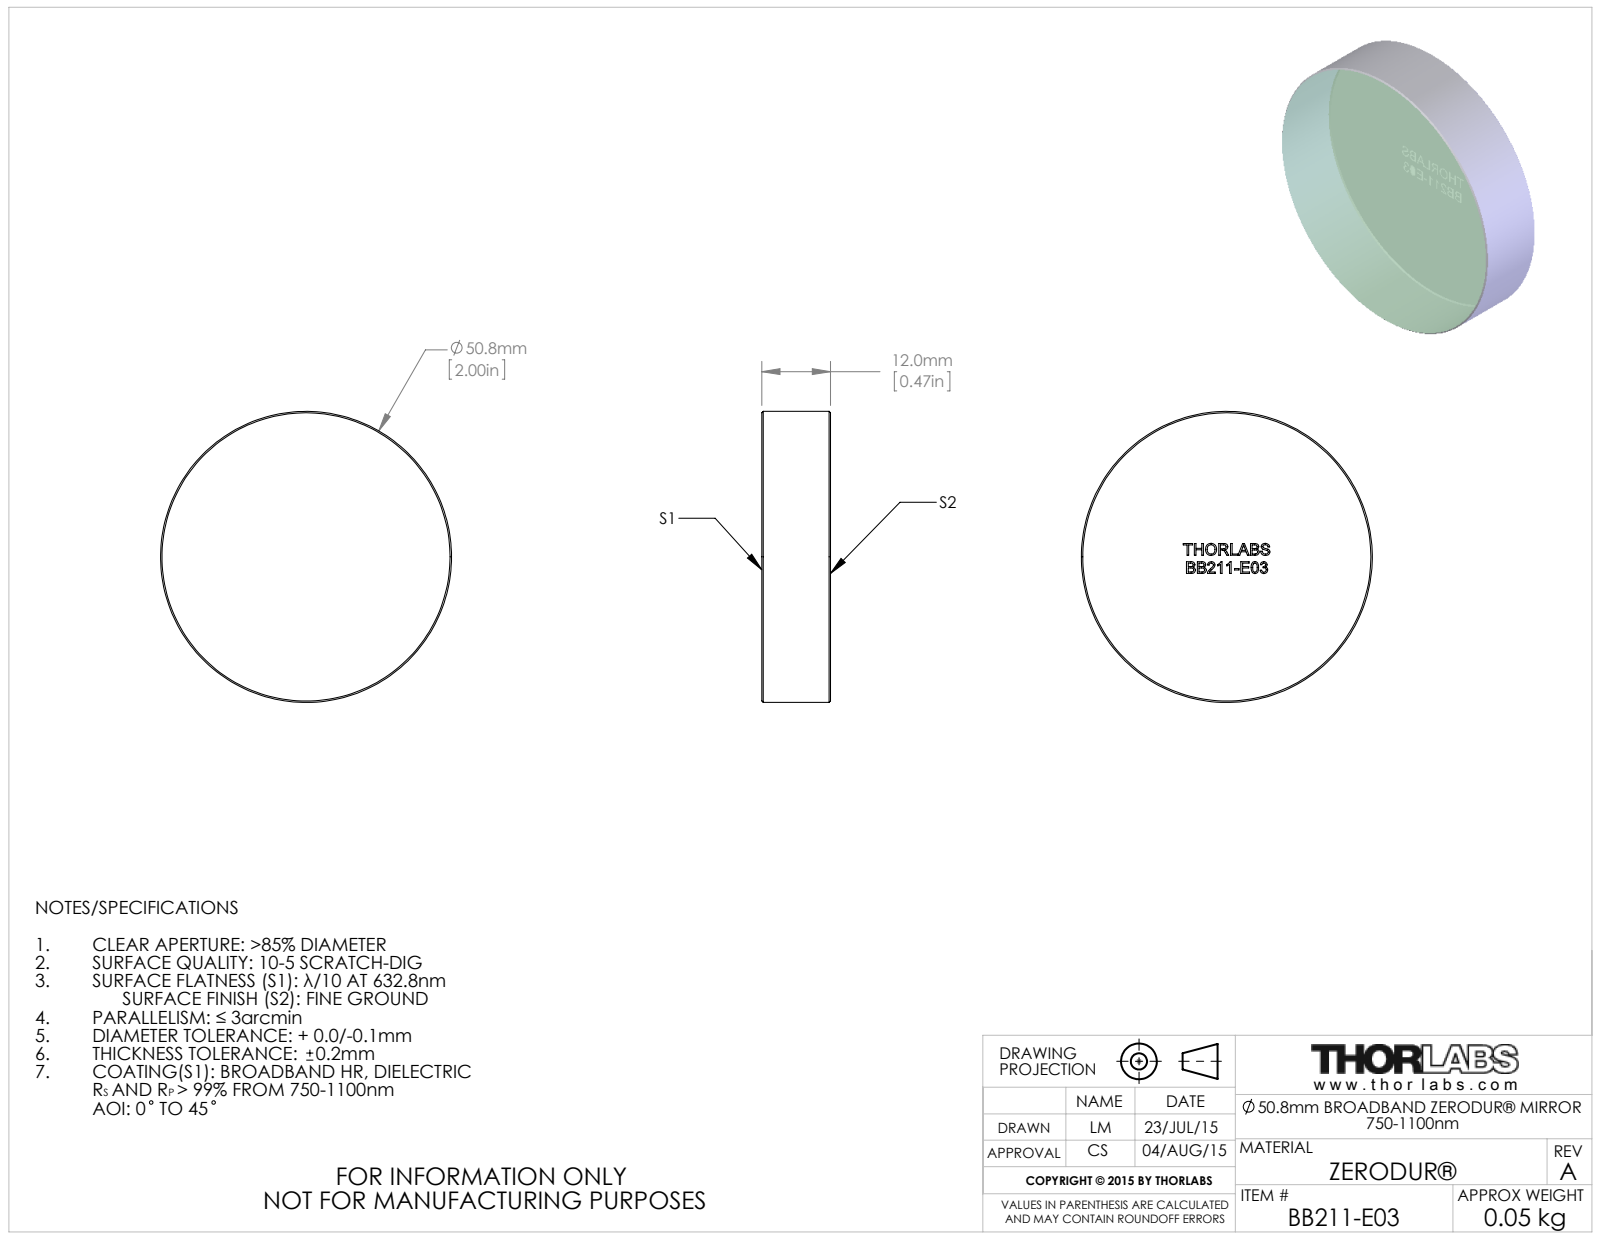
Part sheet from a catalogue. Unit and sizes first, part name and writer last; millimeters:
Units: millimetres
Overall size (bounding box): 50.8 × 50.8 × 12
Round bosses / shafts (diameter × count): ⌀50.8 ×1
Main face-to-face distances: 12, 3.16, 1.58, 2.05, 5.53, 4.03, 7.59, 0.87, 7.68, 1.35
Volume: 24 312 mm³ · Surface area: 5 922 mm²
Bodies: 1 solid, 244 faces (139 planar, 2 cylindrical, 103 other)
Part name (STEP PRODUCT): TTN045206-E0W
STEP written by: SolidWorks 2014 (CONFIG_CONTROL_DESIGN)
